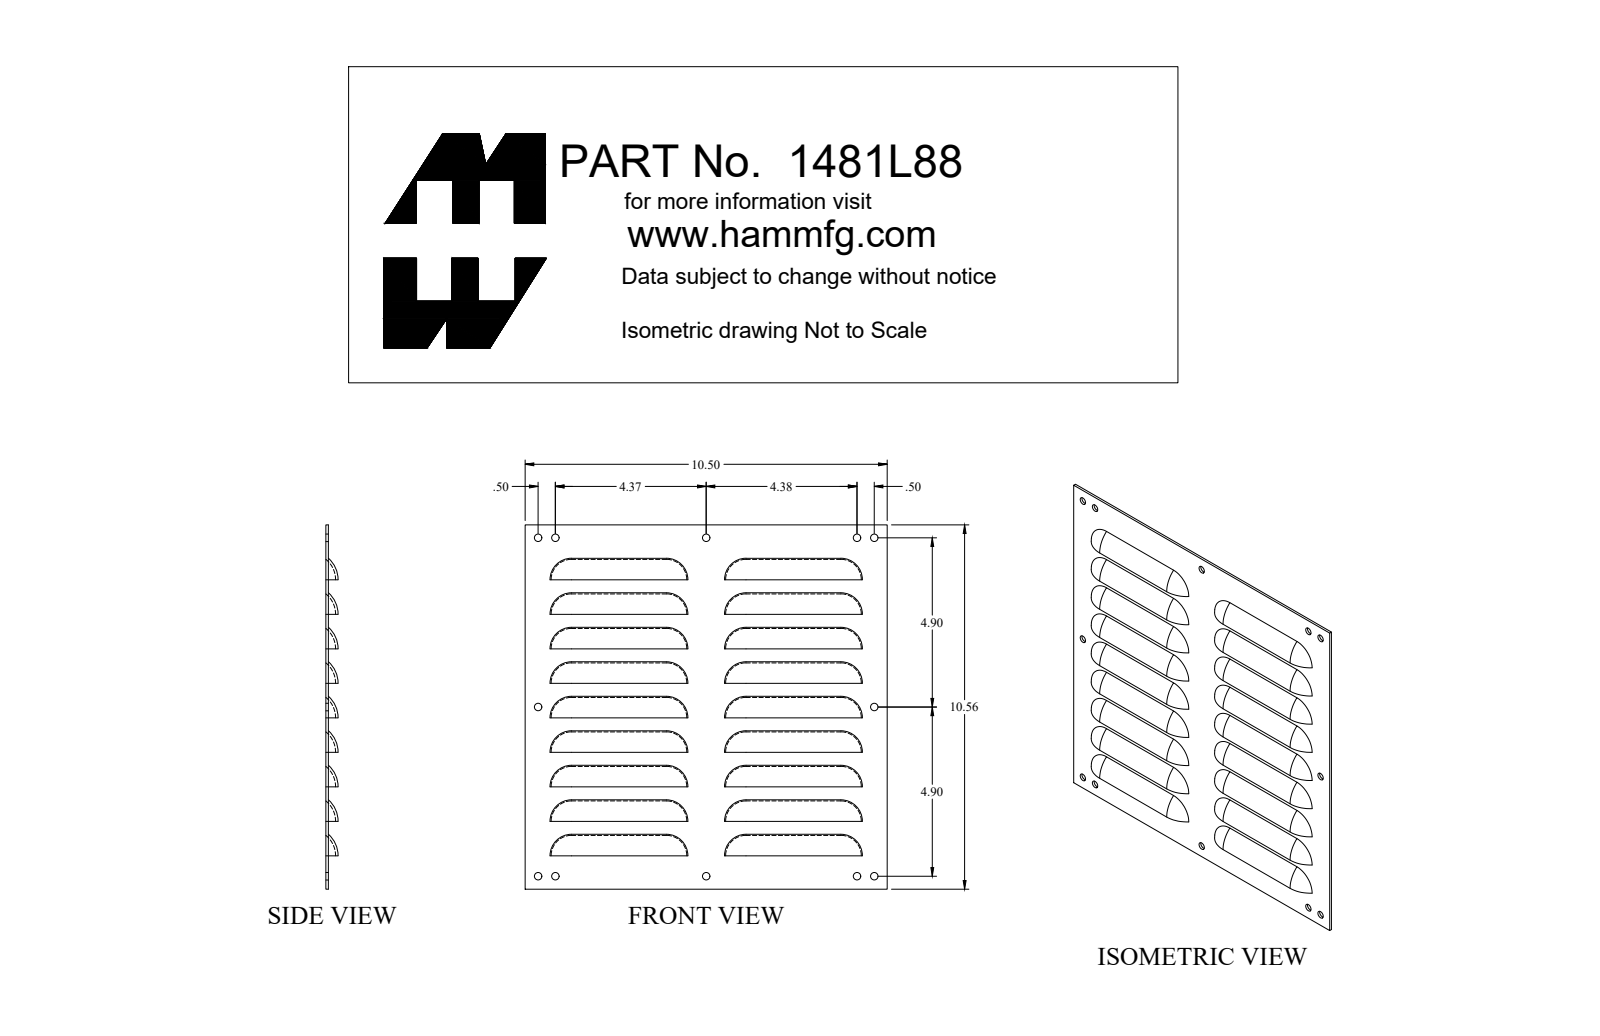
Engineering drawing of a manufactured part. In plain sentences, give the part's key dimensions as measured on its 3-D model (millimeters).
The part is named "1481L88_Default". Its 3-D file was written by "SolidWorks 2019 (CONFIG_CONTROL_DESIGN)". It is 1 solid with 174 faces: 42 planar, 60 cylindrical and 72 other. Overall it measures 268.2 by 266.7 by 9 millimeters. Its volume is 137 800 cubic millimeters and its surface area 159 600 square millimeters. Round holes: 12 of diameter 5.5. Partial cylindrical surfaces (rounded edges, fillets, slot ends): 9 of radius 19.4, 9 of radius 21.2. The main face-to-face distances are 1.8, 25.4, 50.8, 76.2, 101.6, 127, 152.4, 177.8, 203.2, 266.7. The hole center spacings are 249.2, 12.7, 111.1, 123.8, 124.6, 125.2, 175.6, 235.
